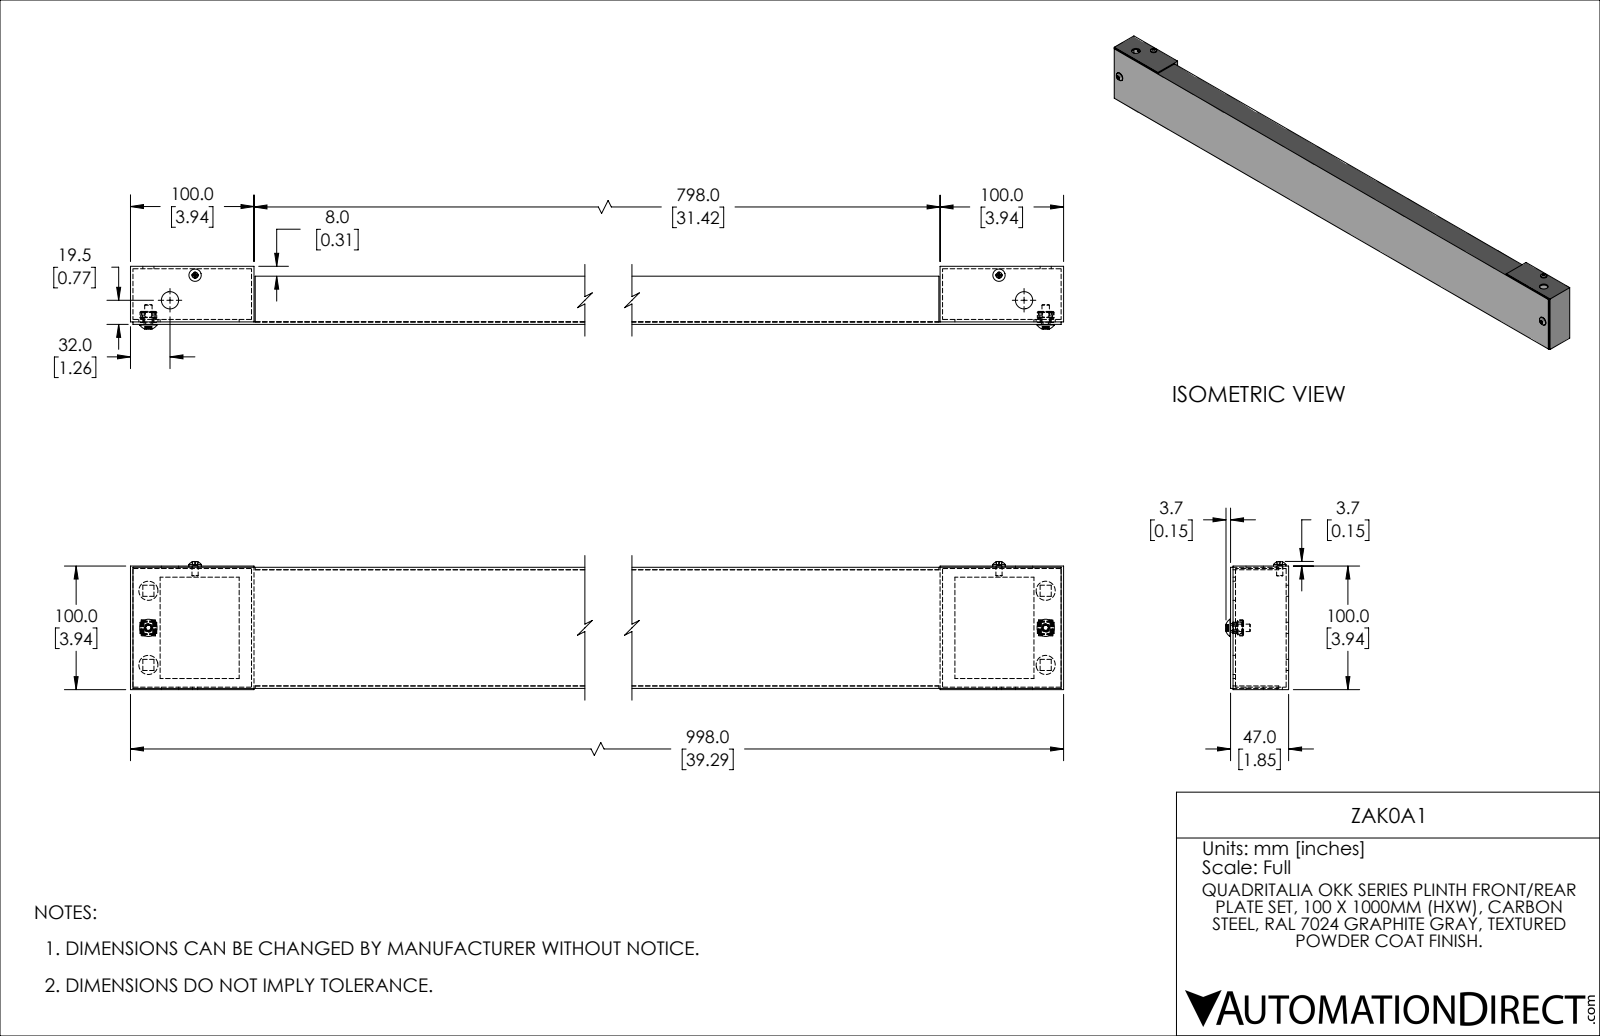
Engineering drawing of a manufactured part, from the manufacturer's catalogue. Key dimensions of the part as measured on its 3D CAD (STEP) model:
Part name (STEP PRODUCT): ZAK0A1
STEP written by: SolidWorks 2021 (CONFIG_CONTROL_DESIGN)
Units: inches
Bodies: 11 solids, 392 faces (242 planar, 132 cylindrical, 18 other)
Overall size (bounding box): 39.291 × 4.084 × 1.996
Volume: 26.56 in³ · Surface area: 687.7 in²
Round holes (diameter × count): ⌀0.61 ×4, ⌀0.167 ×2, ⌀0.194 ×2, ⌀0.276 ×2, ⌀0.551 ×2
Round bosses / shafts (diameter × count): ⌀0.551 ×2, ⌀0.394 ×2, ⌀0.236 ×2, ⌀0.197 ×2
Partial cylindrical surfaces — rounded edges, fillets, slot ends (radius × count): R0.02 ×42, R0.01 ×28, R0.039 ×18
Main face-to-face distances: 0.079, 3.78, 3.858, 0.039, 1.772, 3.819, 3.701, 1.693, 1.85, 0.118
Hole centre spacings: 1.181, 38.168, 38.15, 1.13, 2.362, 35.981, 38.223, 35.173
